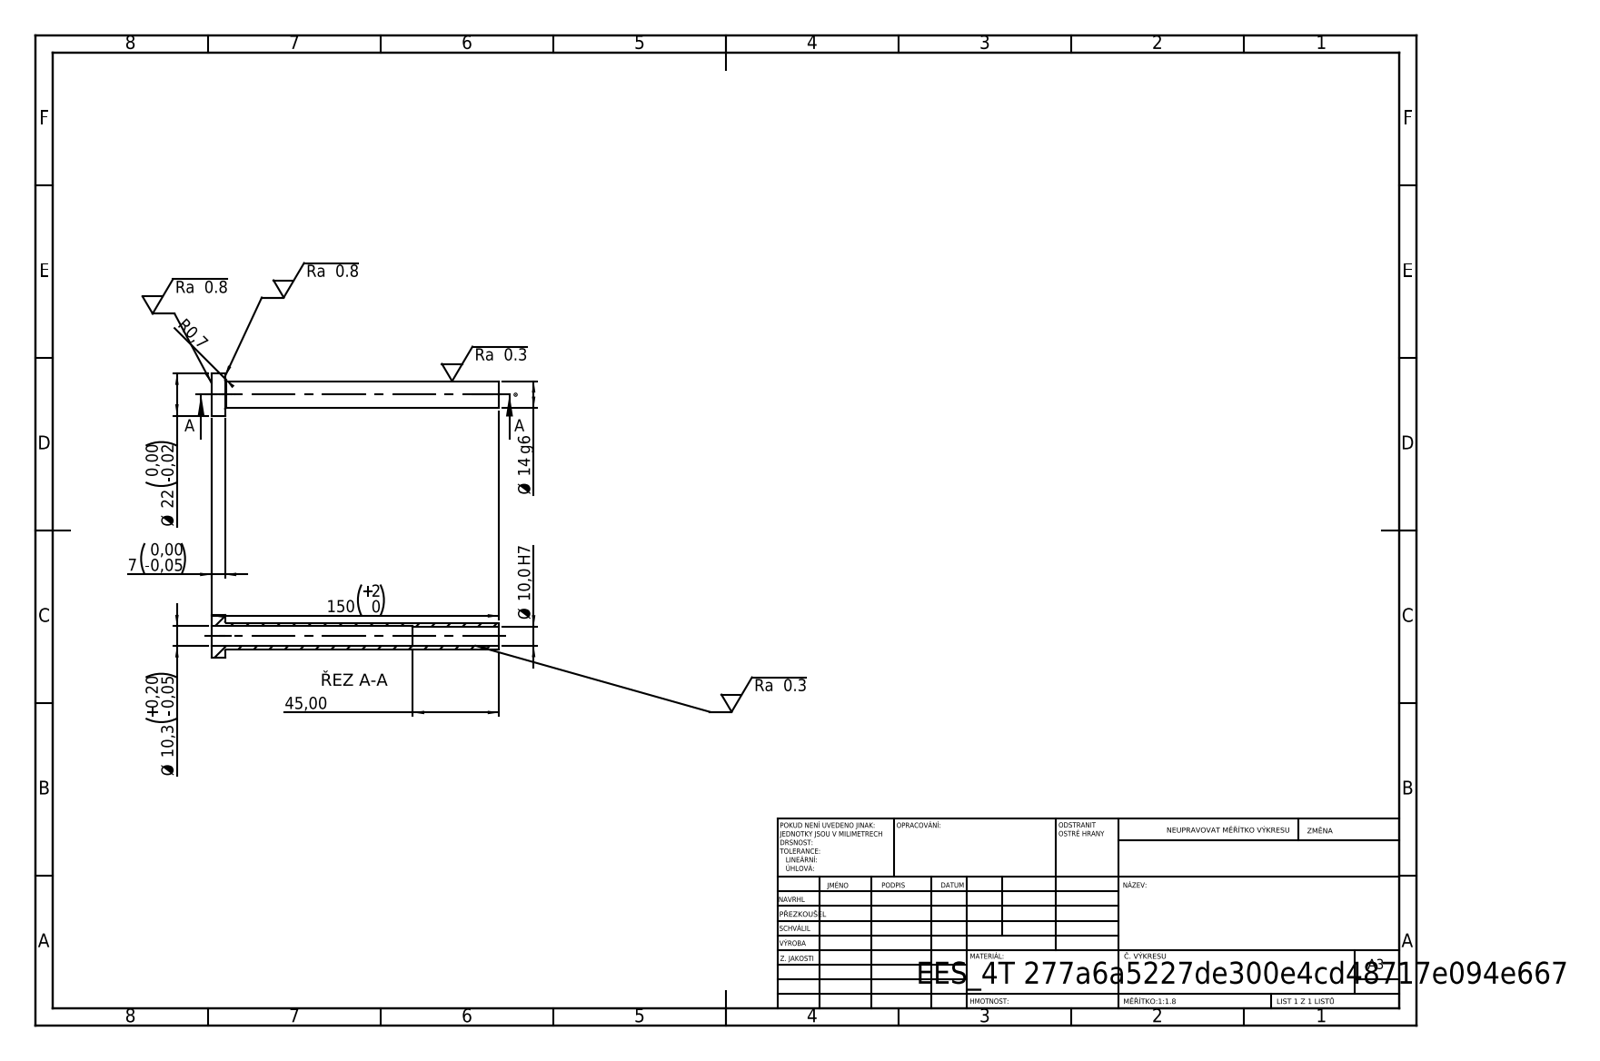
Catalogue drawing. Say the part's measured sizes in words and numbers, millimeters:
Its 3-D file was written by "SolidWorks 2019 (CONFIG_CONTROL_DESIGN)". It is 1 solid with 14 faces: 4 planar, 8 cylindrical and 2 other. Overall it measures 150 by 22 by 22 millimeters. Its volume is 12 396 cubic millimeters and its surface area 12 175 square millimeters. Round holes: 1 of diameter 10, 1 of diameter 10.3. Round bosses or shafts: 1 of diameter 22, 1 of diameter 14. The main face-to-face distances are 7, 150, 143, 105, 98, 45.
